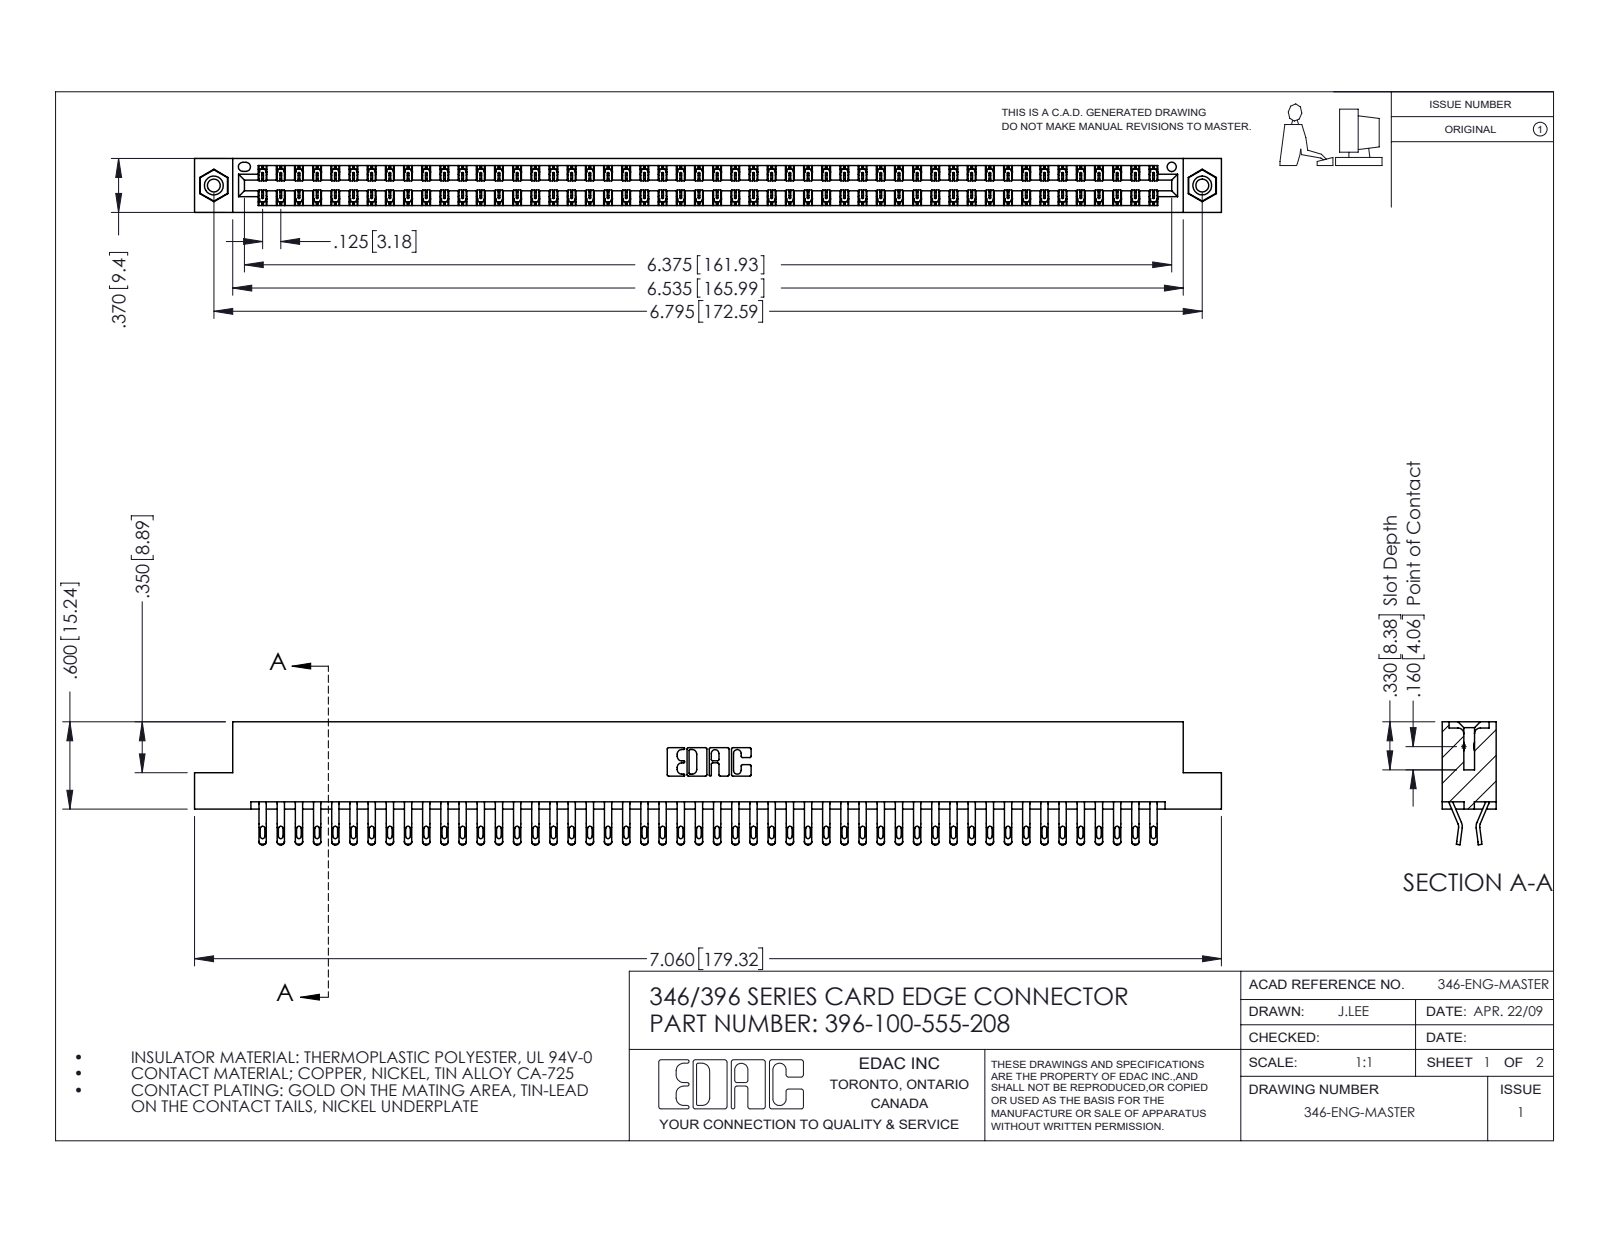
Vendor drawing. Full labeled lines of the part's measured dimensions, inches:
Part name (STEP PRODUCT): 346 Part_Flush Mounting Lugs - 0.156 Dia-TI; 345-250-001_345-250-003-102; 345-292-001_555 Tail; 396-100-555-208
STEP written by: SolidWorks 2016 (CONFIG_CONTROL_DESIGN)
Units: inches
Bodies: 103 solids, 5982 faces (3408 planar, 2558 cylindrical, 16 other)
Overall size (bounding box): 7.06 × 0.845 × 0.37
Volume: 1.088 in³ · Surface area: 39.82 in²
Round holes (diameter × count): ⌀0.089 ×2, ⌀0.125 ×2, ⌀0.156 ×2, ⌀0.064 ×1
Round bosses / shafts (diameter × count): ⌀0.155 ×2
Partial cylindrical surfaces — rounded edges, fillets, slot ends (radius × count): R0.016 ×200, R0.02 ×200, R0.006 ×150, R0.01 ×22, R0.007 ×6, R0.031 ×6, R0.026 ×3, R0.01 ×2
Main face-to-face distances: 0.048, 0.322, 0.37, 0.25, 0.025, 0.072, 0.298, 0.275, 0.148, 0.222
Hole centre spacings: 0.246, 6.586, 6.795
